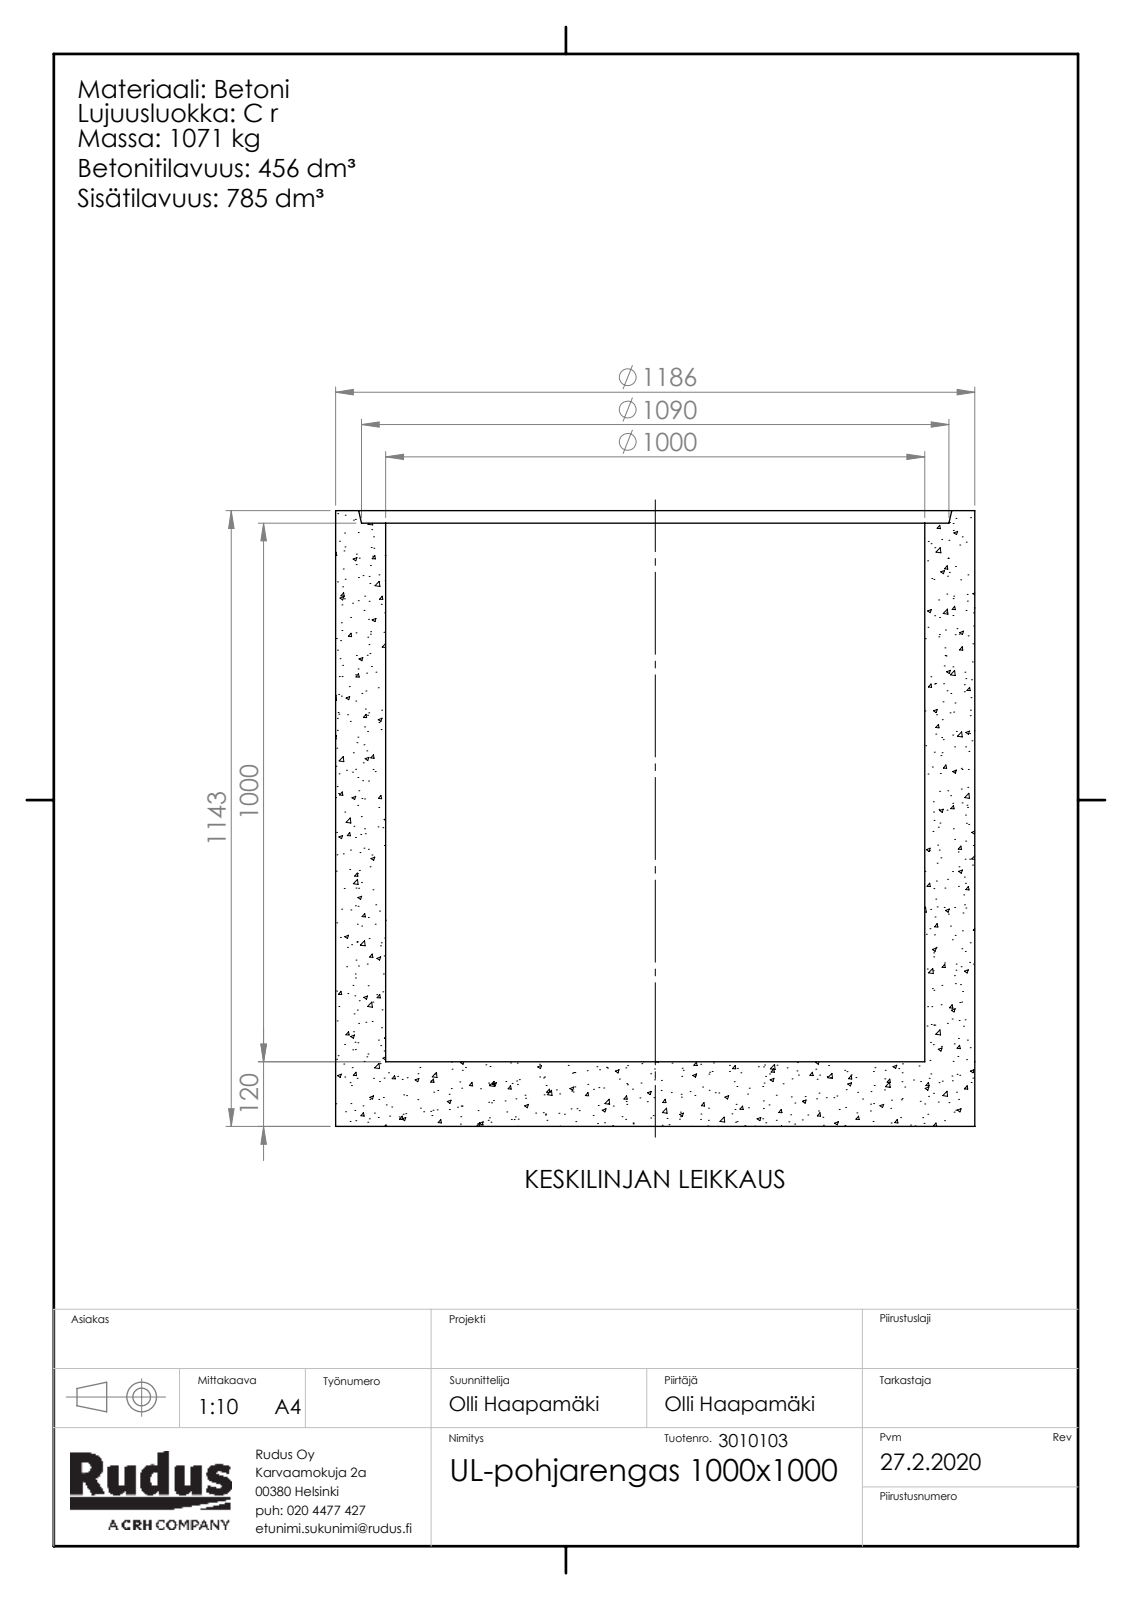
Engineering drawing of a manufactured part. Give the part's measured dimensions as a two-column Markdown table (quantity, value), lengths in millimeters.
| quantity | value |
| --- | --- |
| part name | EK-osa-kaivorunko_UL-pohjarengas; Rudus 3010103 UL-pohjarengas 1000x1000 |
| STEP written by | SolidWorks 2019 (CONFIG_CONTROL_DESIGN) |
| units | millimeters |
| bodies | 1 solid, 89 faces (4 planar, 2 cylindrical, 83 other) |
| overall size | 1186 × 1186 × 1143 |
| volume | 455 700 000 mm³ |
| surface area | 9 678 000 mm² |
| round bosses / shafts (diameter × count) | 1186 × 1 |
| main face-to-face distances | 120, 1143, 1023, 1120, 1000, 23 |
